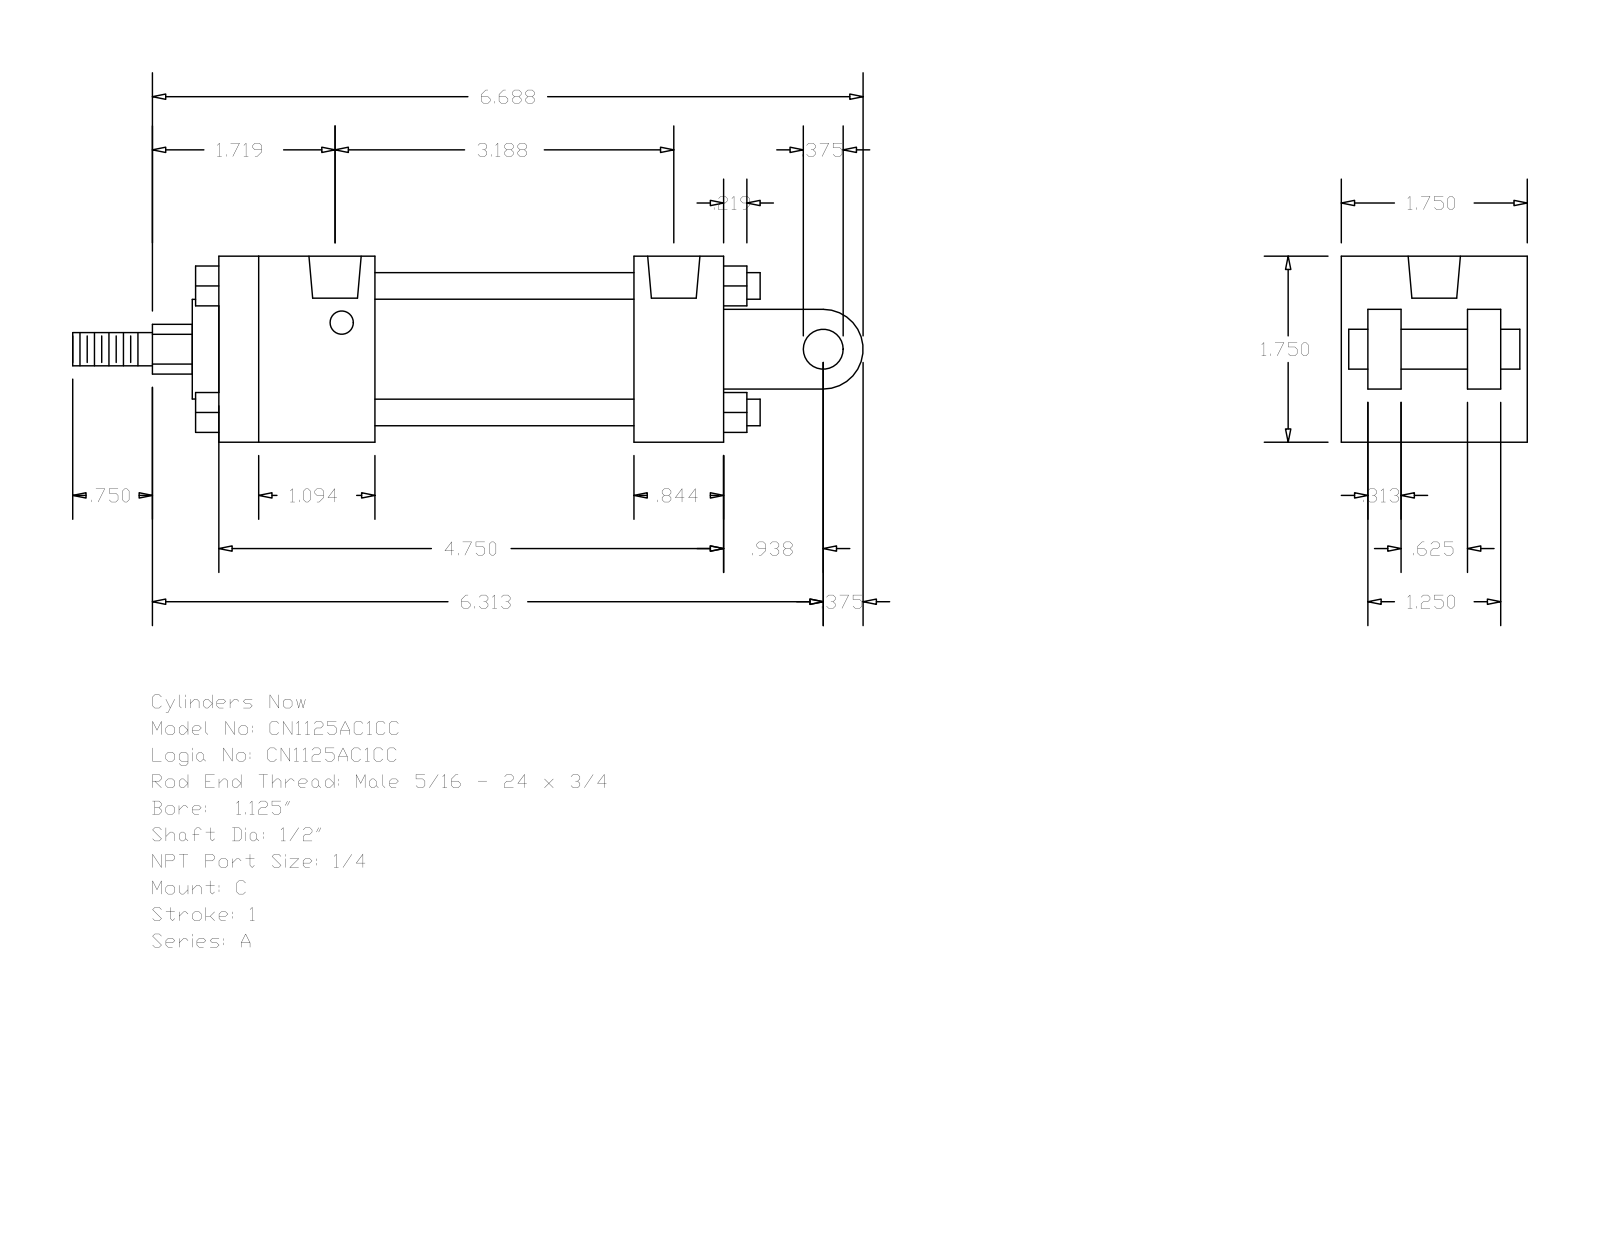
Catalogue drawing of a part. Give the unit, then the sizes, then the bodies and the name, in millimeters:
Units: millimetres
Overall size (bounding box): 188.91 × 44.45 × 44.45
Round holes (diameter × count): ⌀5.56 ×4, ⌀12.49 ×2
Round bosses / shafts (diameter × count): ⌀6.35 ×4, ⌀31.88 ×1, ⌀23.81 ×1, ⌀12.7 ×1, ⌀9.53 ×1, ⌀7.94 ×1
Partial cylindrical surfaces — rounded edges, fillets, slot ends (radius × count): R5.94 ×1, R9.53 ×1
Main face-to-face distances: 44.46, 6.35, 31.76, 14.29, 120.65, 30.17, 99.21, 21.44, 37.3, 61.91
Hole centre spacings: 77.79, 1.58, 1.59, 79.37, 79.38, 80.96
Bodies: 0 solids, 135 faces (102 planar, 33 cylindrical, 0 other)
Part name (STEP PRODUCT): A_C__0112_0.5
STEP written by: GSSL Pune (CONFIG_CONTROL_DESIGN)
